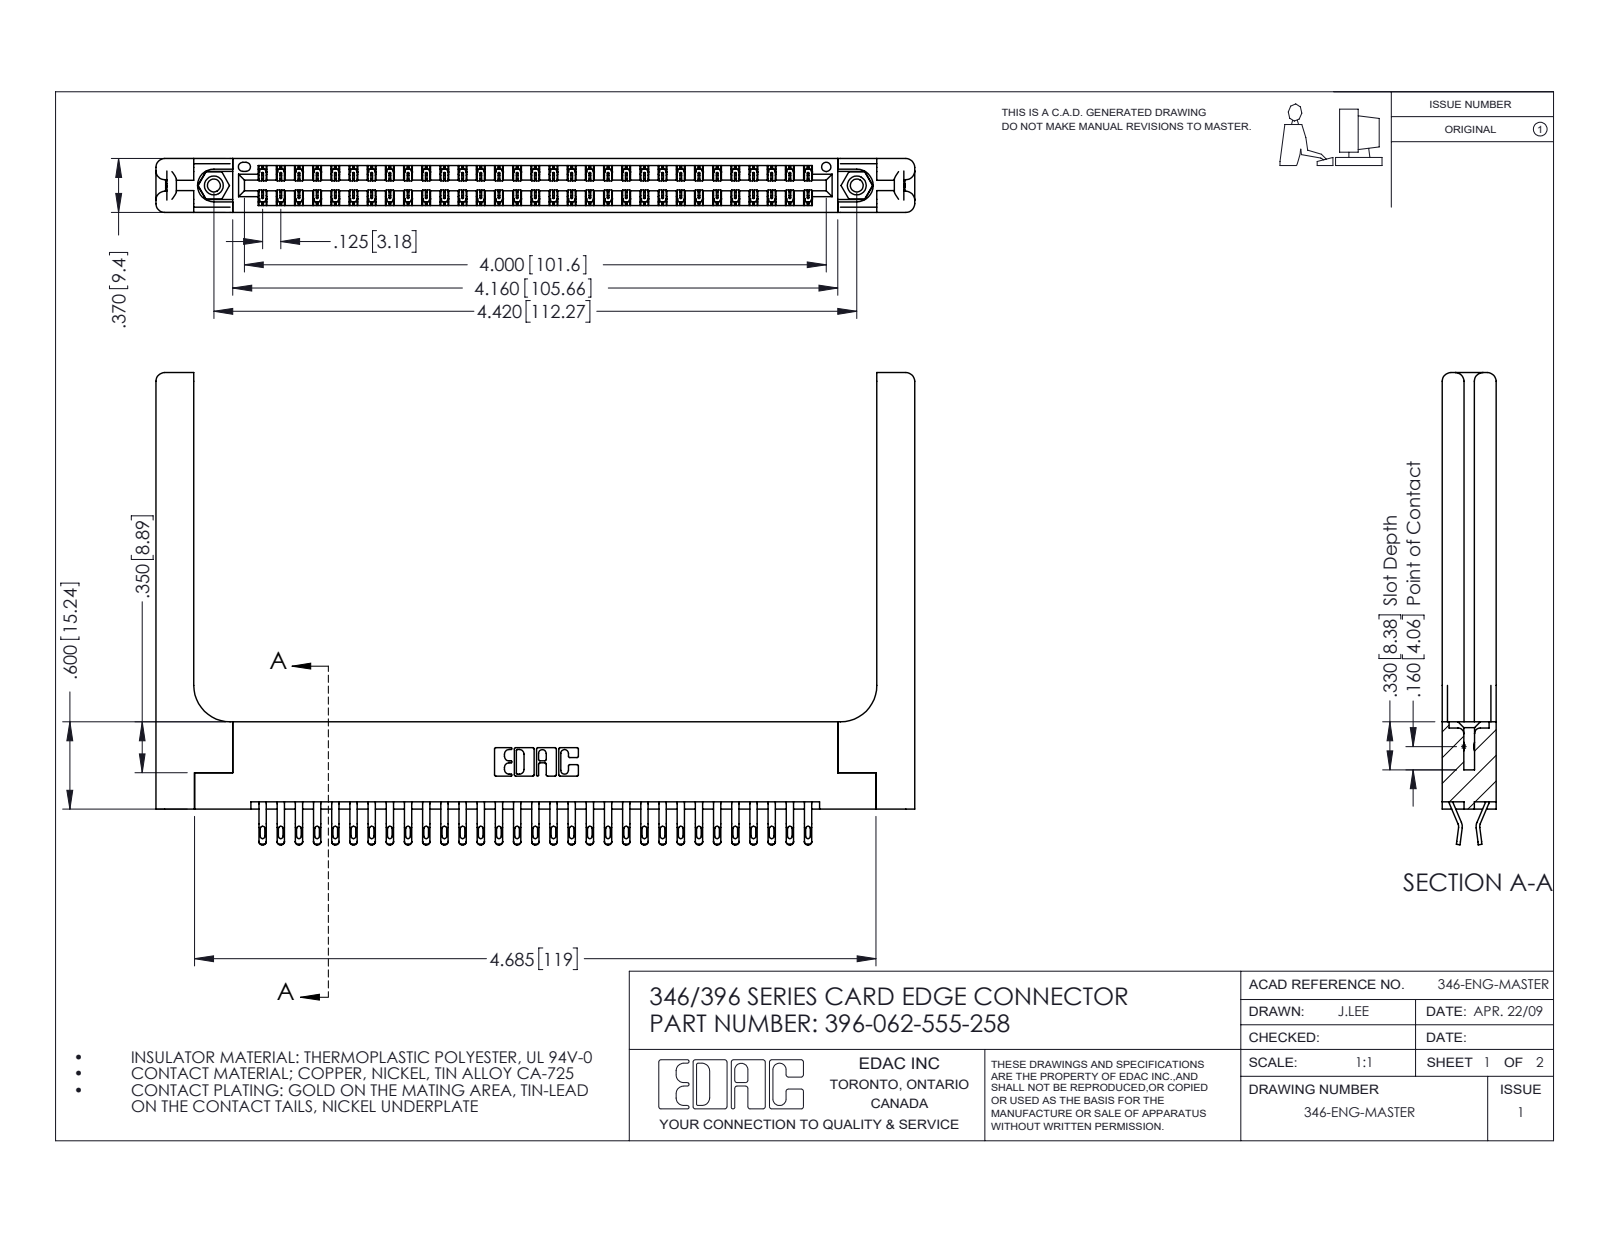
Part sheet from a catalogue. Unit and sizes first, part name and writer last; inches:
Units: inches
Overall size (bounding box): 5.216 × 3.245 × 0.37
Round holes (diameter × count): ⌀0.089 ×2, ⌀0.125 ×2, ⌀0.156 ×2, ⌀0.064 ×1
Round bosses / shafts (diameter × count): ⌀0.155 ×2
Partial cylindrical surfaces — rounded edges, fillets, slot ends (radius × count): R0.016 ×124, R0.02 ×124, R0.006 ×93, R0.01 ×22, R0.06 ×16, R0.007 ×6, R0.031 ×6, R0.026 ×3
Main face-to-face distances: 0.37, 0.048, 0.322, 0.072, 0.148, 0.15, 0.25, 0.025, 0.298, 0.275
Hole centre spacings: 0.246, 4.212, 4.42
Volume: 1.251 in³ · Surface area: 36.16 in²
Bodies: 67 solids, 3974 faces (2270 planar, 1644 cylindrical, 60 other)
Part name (STEP PRODUCT): 396-062-555-258; 345-292-001_555 Tail; 346-220-058_345-220-058; 346 Part_Flush Mounting Lugs - 0.156 Dia-TH (+1 more)
STEP written by: SolidWorks 2016 (CONFIG_CONTROL_DESIGN)
